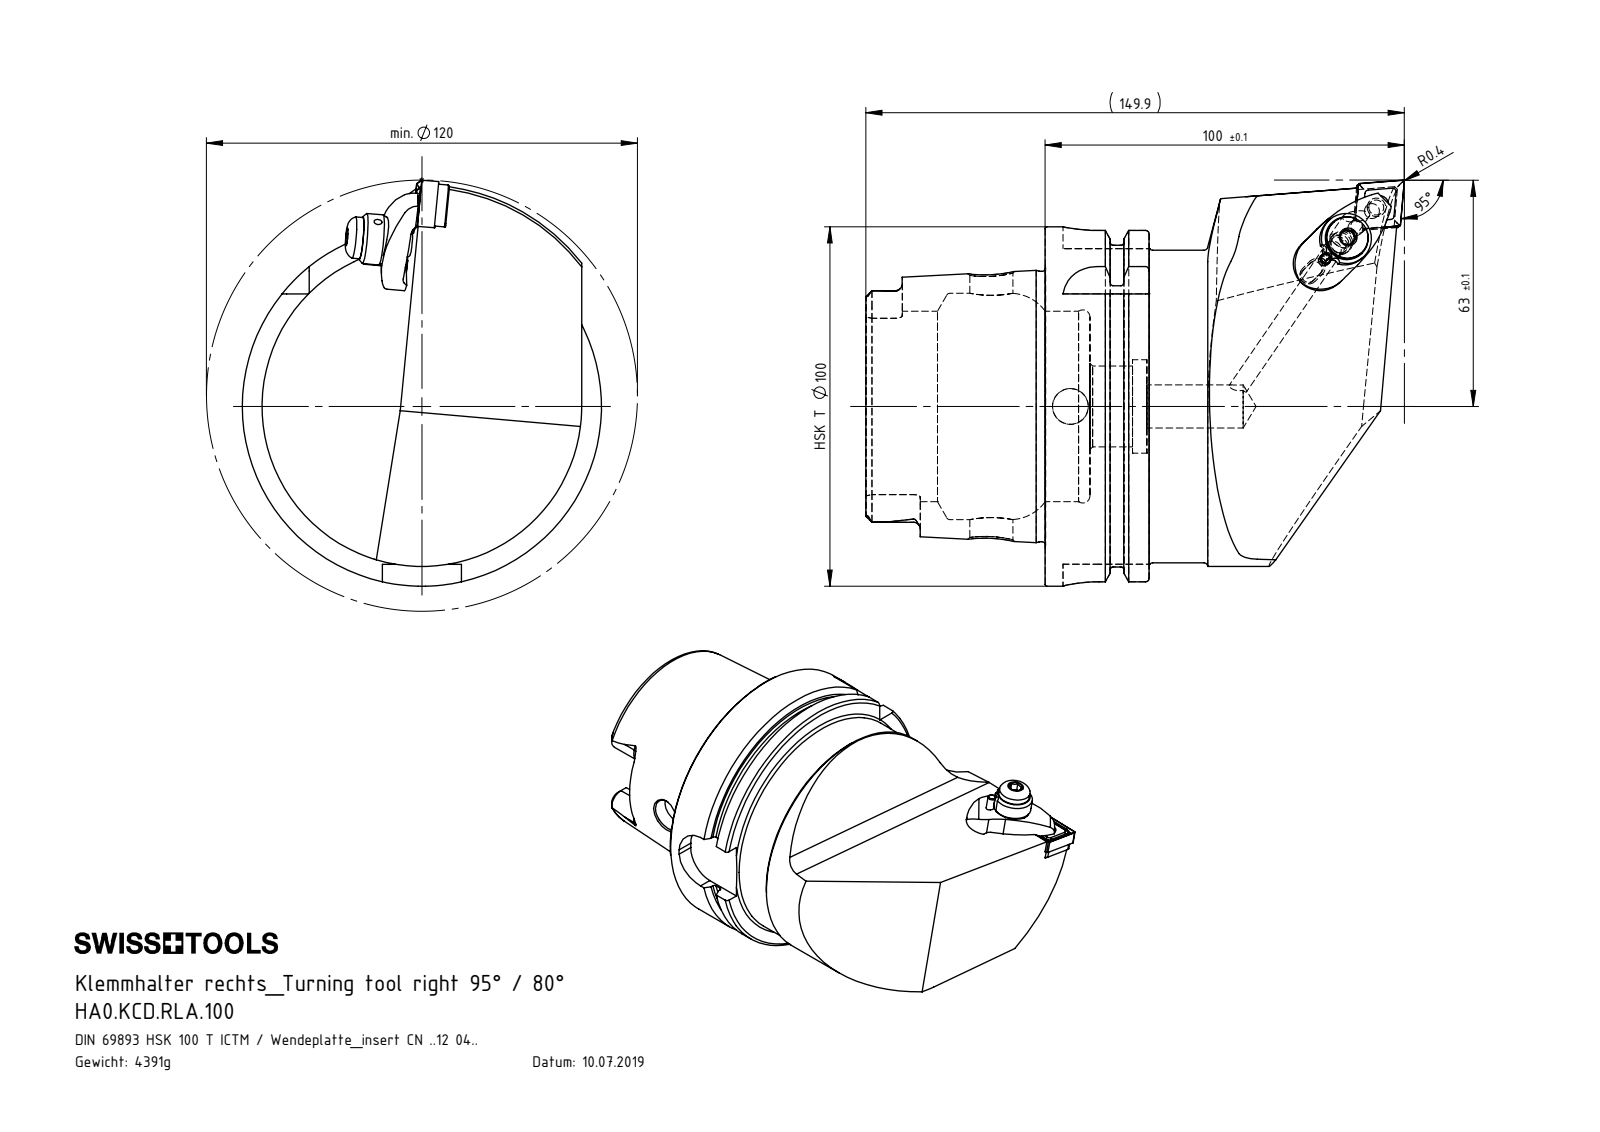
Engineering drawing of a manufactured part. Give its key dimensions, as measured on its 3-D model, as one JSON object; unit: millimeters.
{"part_name": "WCD-ER2.101.003_A; WCC-ER5.102.012_B; WCC-ER4.103.032_A; WCC-ER3.102.024_C (+7 more)", "step_written_by": "SolidWorks 2017 (AUTOMOTIVE_DESIGN)", "units": "millimeters", "bodies": {"solids": 11, "faces": 468, "planar": 120, "cylindrical": 154, "other": 194}, "overall_size": [149.9, 113, 100], "volume_mm3": 558584, "surface_area_mm2": 74289, "round_holes": [[2, 3], [4.2, 2], [5, 2], [7, 2], [12, 2], [2.4, 1], [3, 1], [4, 1], [5.16, 1], [6, 1], [6.2, 1], [6.55, 1]], "round_bosses_or_shafts": [[5, 2], [3, 2], [100, 1], [91.95, 1], [87, 1], [75.26, 1], [14, 1], [11.5, 1]], "partial_cylinders_radius": [[0.39, 6], [0.69, 6], [1.9, 6], [0.4, 4], [1, 4], [10, 4], [1.5, 3], [2, 2]], "face_to_face_distances": [12.45, 28.95, 16.5, 49.9, 62.35, 78.85, 87.8, 78.2, 28.3, 15.85], "hole_center_spacings": [8.01, 8.19, 14.67, 14.93, 22.94, 6.48, 6.66, 6.68]}
